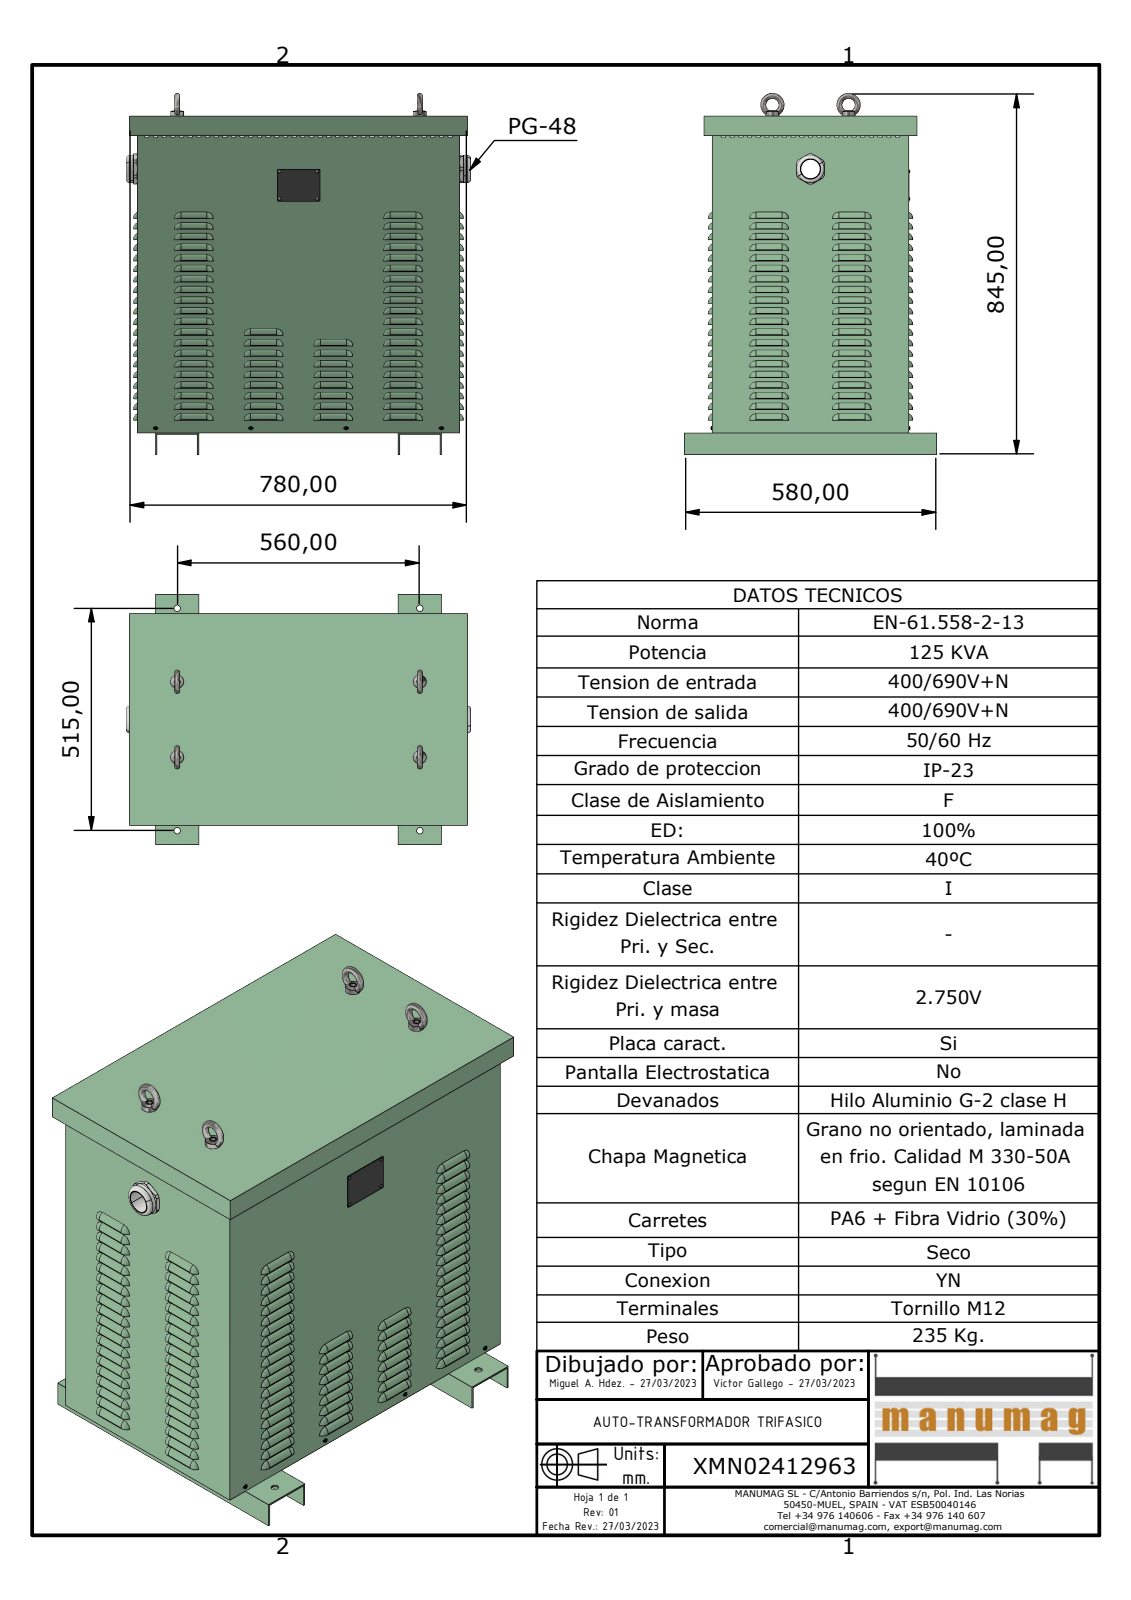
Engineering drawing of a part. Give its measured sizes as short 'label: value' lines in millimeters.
name: XMN02412963; JE125 - JE160NACIONAL CUERPO; JE125 JE160 NACIONAL BASE; JE125 - JE160 NACIONAL PATA (+6 more)
written by: Autodesk Inventor 2023 (AUTOMOTIVE_DESIGN)
unit: mm
bodies: 24 solids, 4123 faces (1445 planar, 1686 cylindrical, 992 other)
size: 835 × 795.27 × 580
volume: 6 672 000 mm³; area: 5 912 000 mm²
holes: 780× ⌀11, 8× ⌀15, 4× ⌀4, 4× ⌀5, 4× ⌀10.11, 1× ⌀44, 1× ⌀60
bosses: 4× ⌀30, 4× ⌀4, 4× ⌀3.62, 4× ⌀3.2, 1× ⌀63, 1× ⌀59.3, 1× ⌀59.15, 1× ⌀57.63
rounds: 194× R14, 80× R7, 80× R15, 8× R2.5, 4× R2, 1× R35
face distances: 2, 450, 730, 742, 448, 452, 732, 740, 728, 744
hole spacings: 20.79, 164.63, 33.28, 149.69, 179, 30, 47.25, 149
